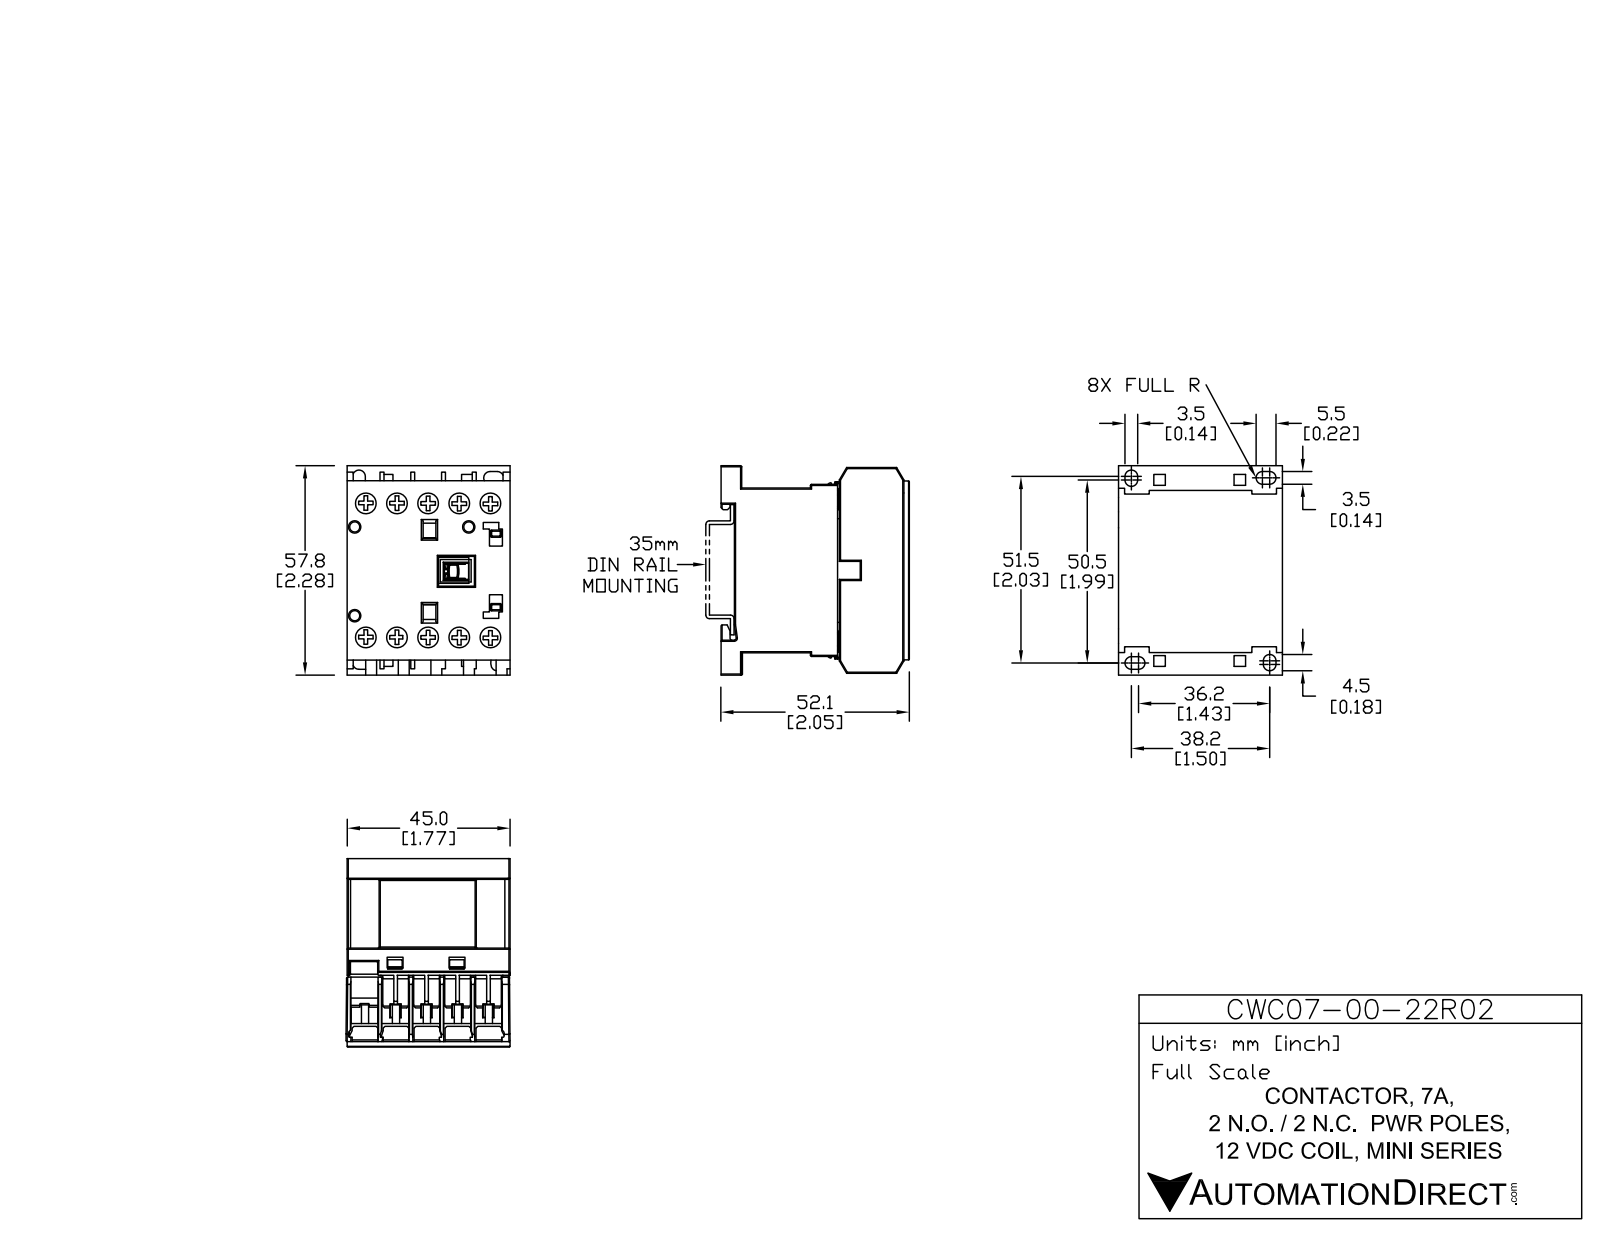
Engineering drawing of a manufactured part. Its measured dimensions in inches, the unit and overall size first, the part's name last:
Units: inches
Overall size (bounding box): 2.285 × 2.052 × 1.801
Round holes (diameter × count): ⌀0.244 ×10, ⌀0.11 ×3
Round bosses / shafts (diameter × count): ⌀0.232 ×10
Partial cylindrical surfaces — rounded edges, fillets, slot ends (radius × count): R0.012 ×20, R0.068 ×6, R0.068 ×2, R0.013 ×1, R0.017 ×1, R0.022 ×1
Main face-to-face distances: 0.325, 1.791, 0.049, 0.65, 0.374, 0.217, 0.699, 0.202, 0.419, 0.276
Hole centre spacings: 0.337, 1.494, 0.673, 1.603, 1.455, 1.01, 1.771, 0.272
Volume: 5.927 in³ · Surface area: 47.18 in²
Bodies: 15 solids, 535 faces (445 planar, 90 cylindrical, 0 other)
Part name (STEP PRODUCT): CWC07-00-22R02
STEP written by: SolidWorks 2013 (AUTOMOTIVE_DESIGN)
